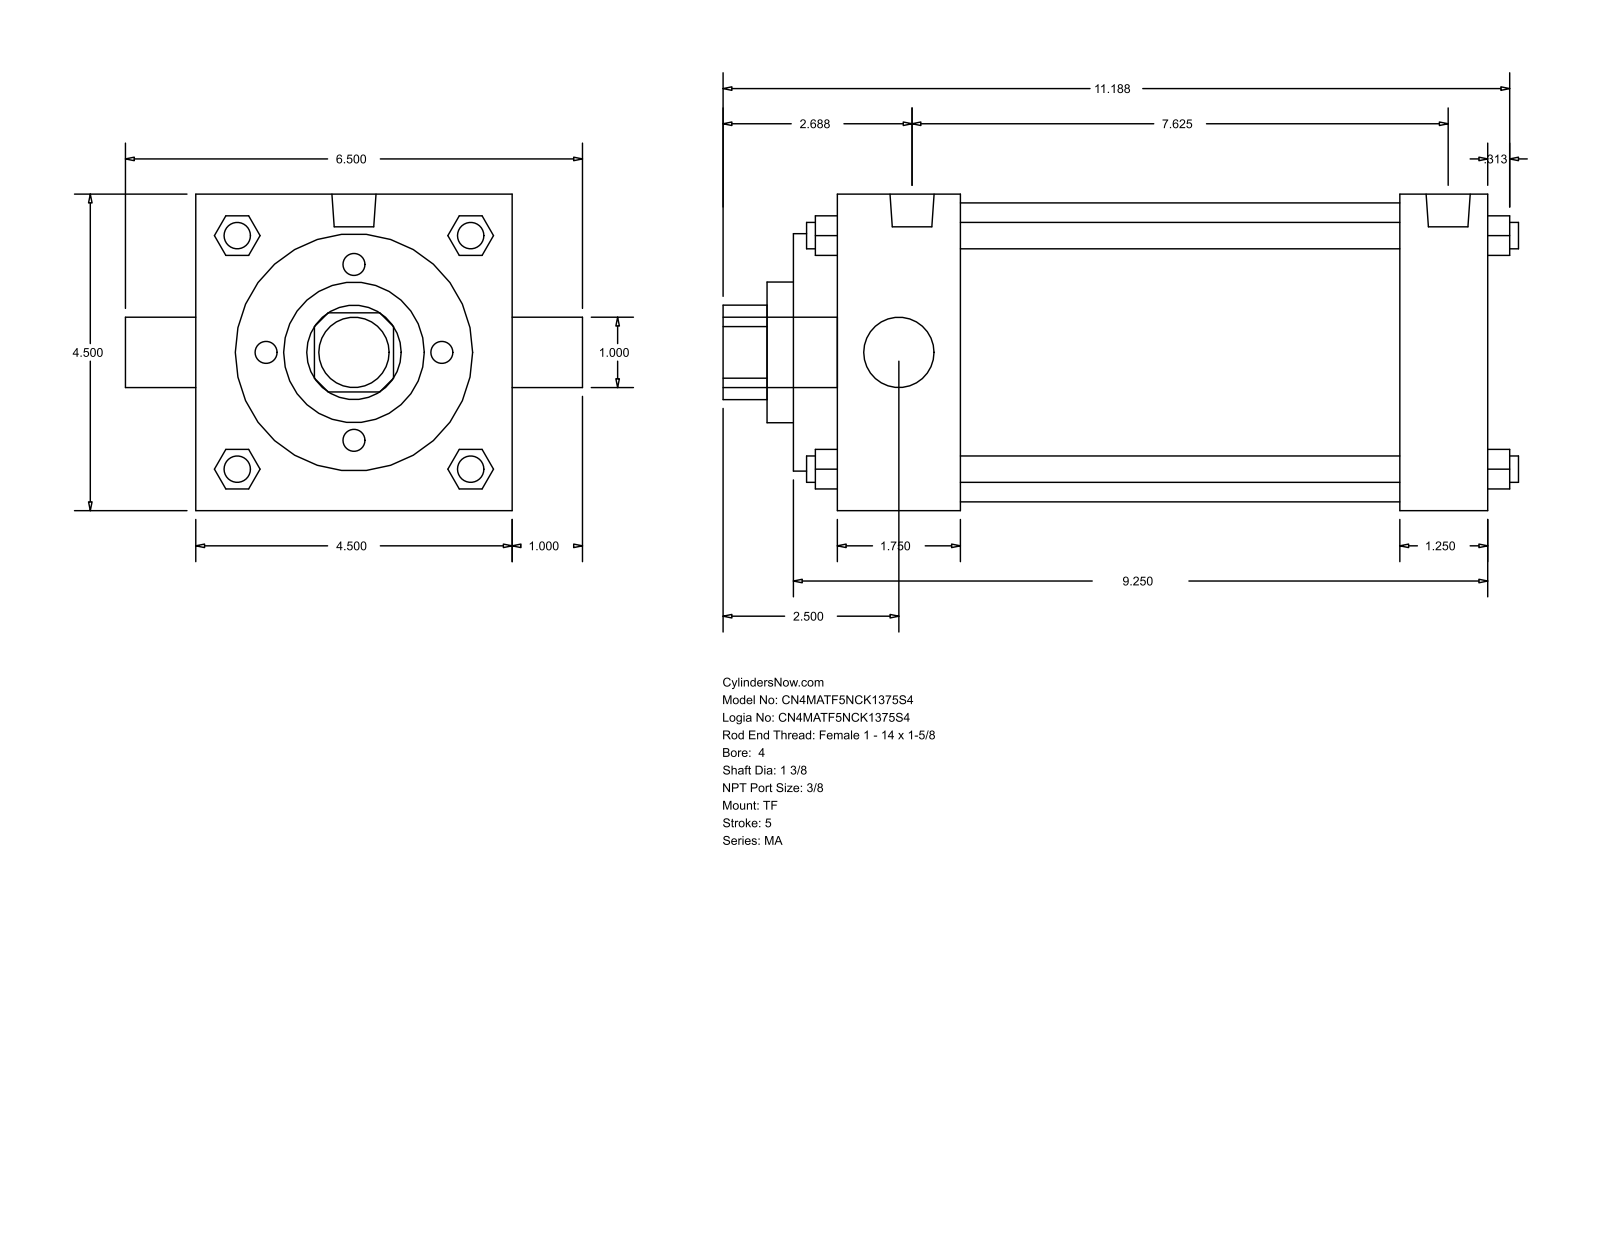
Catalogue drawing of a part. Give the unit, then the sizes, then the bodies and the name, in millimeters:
Units: millimetres
Overall size (bounding box): 287.34 × 165.1 × 114.3
Round holes (diameter × count): ⌀25.4 ×1, ⌀34.92 ×1, ⌀50.8 ×1, ⌀85.72 ×1, ⌀107.95 ×1
Round bosses / shafts (diameter × count): ⌀9.53 ×4, ⌀11.11 ×3, ⌀15.93 ×2, ⌀25.4 ×1
Partial cylindrical surfaces — rounded edges, fillets, slot ends (radius × count): R17.06 ×1
Main face-to-face distances: 114.3, 234.96, 15.87, 250.83, 219.07, 203.2, 31.76, 60.32, 44.45, 158.75
Bodies: 0 solids, 122 faces (93 planar, 29 cylindrical, 0 other)
Part name (STEP PRODUCT): MA_TF__0400_1.375
STEP written by: GSSL Pune (CONFIG_CONTROL_DESIGN)
